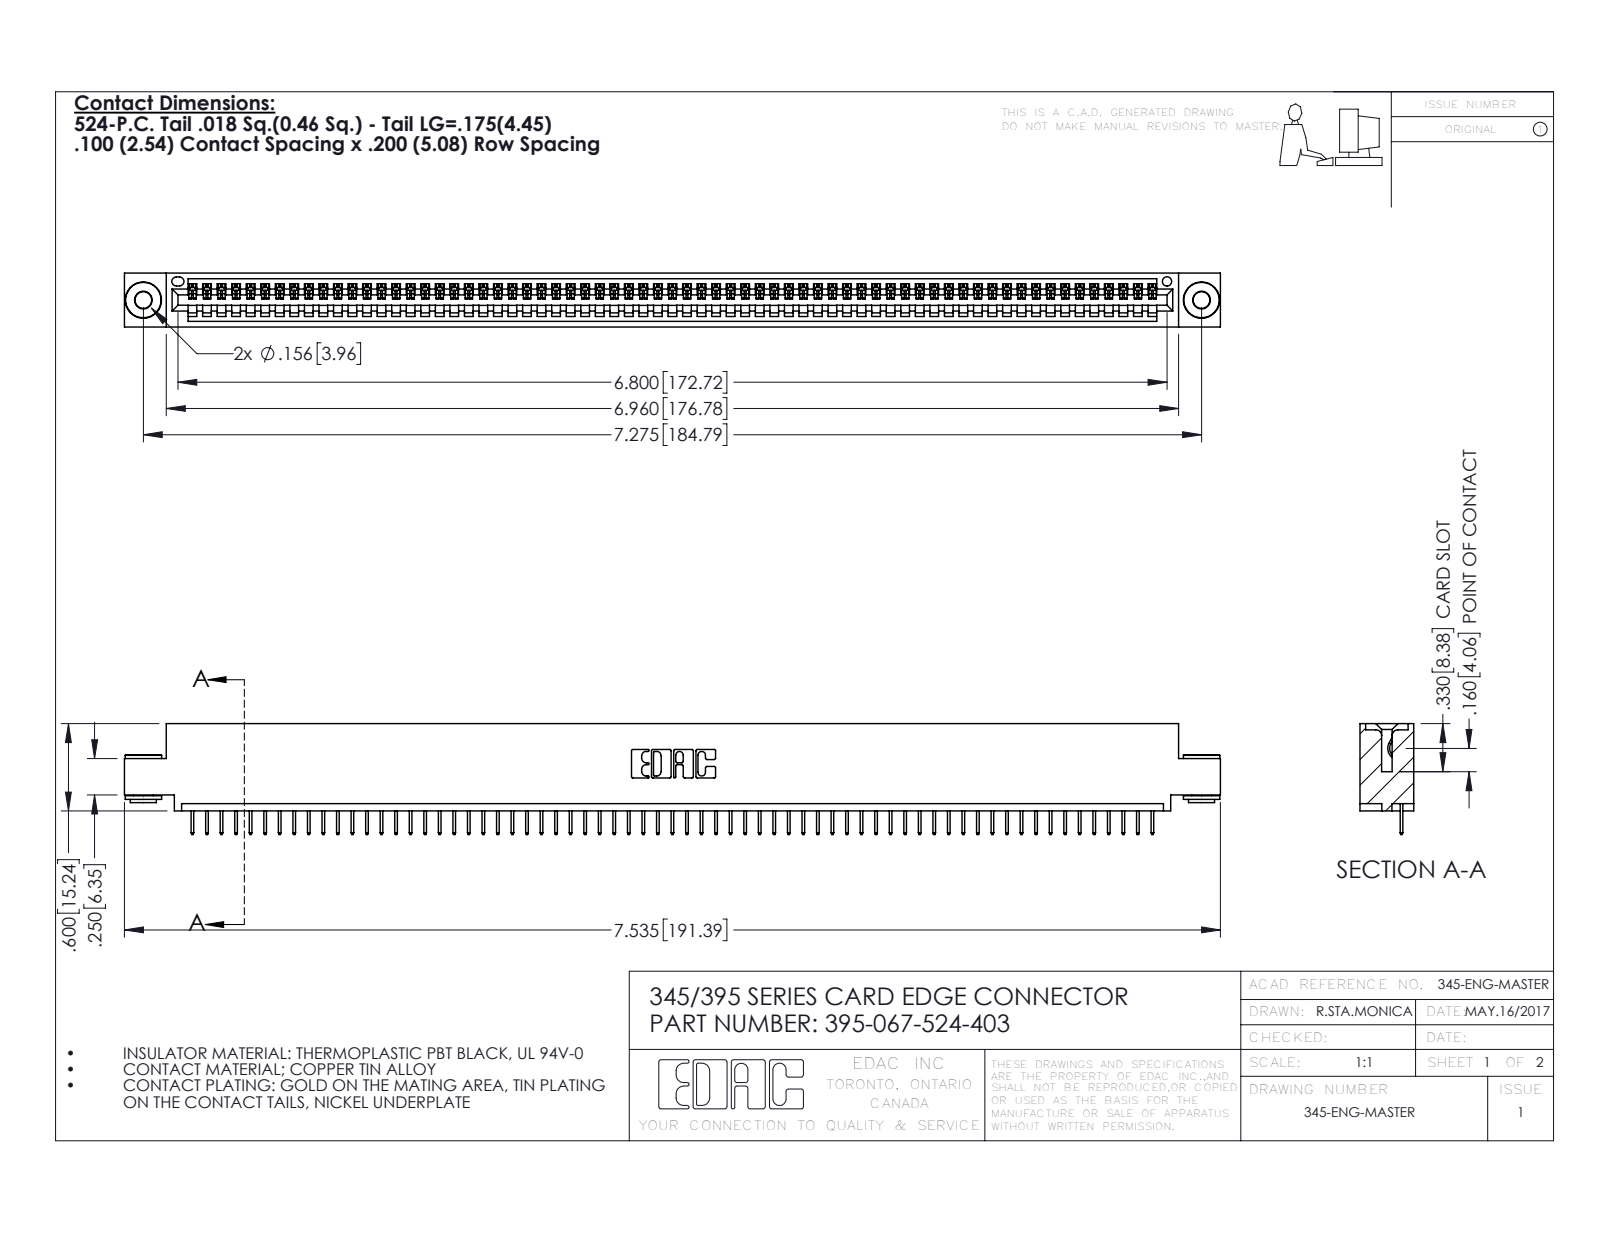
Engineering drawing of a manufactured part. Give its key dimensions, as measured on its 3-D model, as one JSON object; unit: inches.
{"part_name": "345 Part_0.110 Offset - 0.156 Dia-TH; 345-250-002_345-250-002-102; 395-067-524-403; 345-292-001_345-293-124", "step_written_by": "SolidWorks 2016 (CONFIG_CONTROL_DESIGN)", "units": "inches", "bodies": {"solids": 70, "faces": 4322, "planar": 3176, "cylindrical": 1138, "other": 8}, "overall_size": [7.535, 0.762, 0.37], "volume_in3": 1.102, "surface_area_in2": 36.88, "round_holes": [[0.116, 2], [0.156, 2], [0.064, 1]], "round_bosses_or_shafts": [[0.25, 2], [0.18, 2], [0.136, 2]], "partial_cylinders_radius": [[0.006, 134], [0.01, 22], [0.007, 6], [0.031, 6], [0.026, 3], [0.031, 2], [0.04, 2], [0.014, 1]], "face_to_face_distances": [0.072, 0.298, 0.37, 0.2, 0.025, 0.098, 0.272, 0.225, 0.072, 0.149], "hole_center_spacings": [0.27, 7.039, 7.275]}
